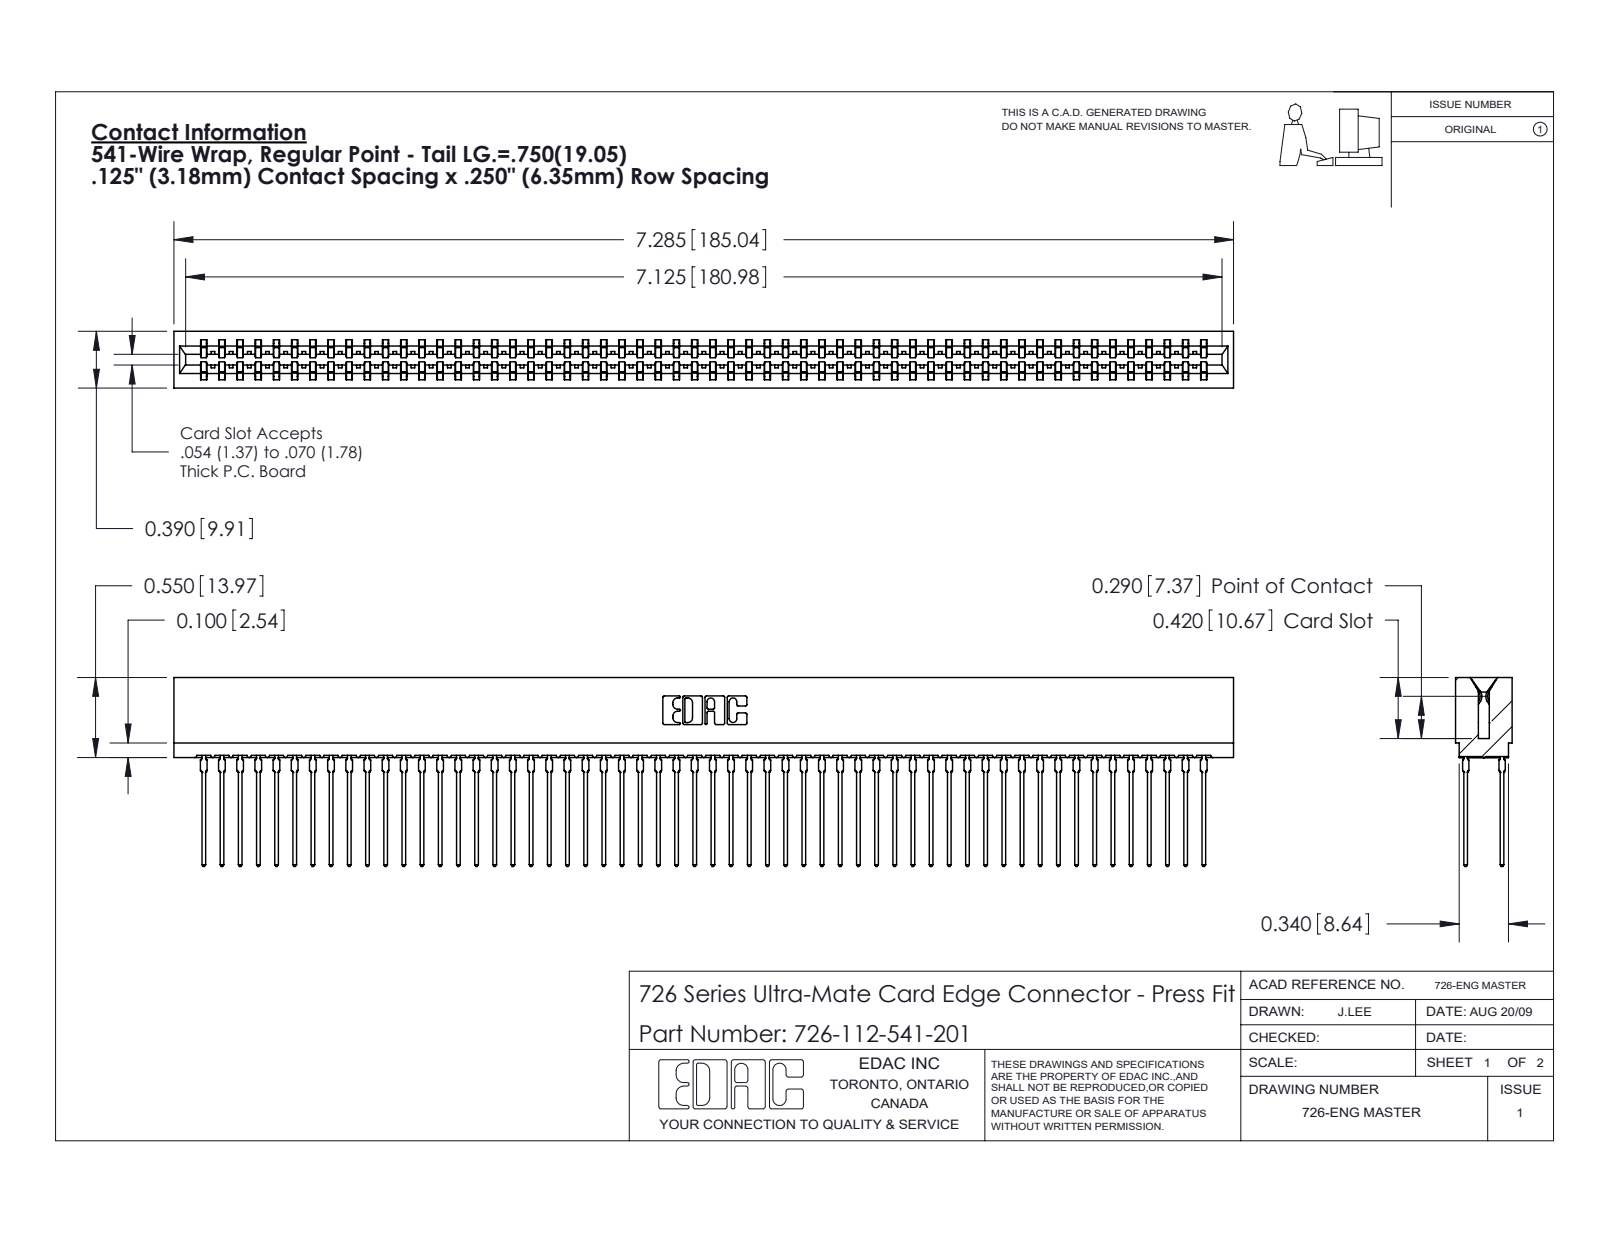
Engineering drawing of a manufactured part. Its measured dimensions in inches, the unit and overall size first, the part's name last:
Units: inches
Overall size (bounding box): 7.285 × 1.299 × 0.39
Partial cylindrical surfaces — rounded edges, fillets, slot ends (radius × count): R0.021 ×224, R0.015 ×57, R0.01 ×22, R0.005 ×8, R0.011 ×8, R0.007 ×6, R0.031 ×6, R0.026 ×3
Main face-to-face distances: 0.057, 0.333, 0.025, 0.307, 0.25, 0.39, 0.083, 0.275, 0.225, 0.365
Volume: 1.072 in³ · Surface area: 50.2 in²
Bodies: 113 solids, 10121 faces (5207 planar, 2002 cylindrical, 2912 other)
Part name (STEP PRODUCT): 746-292-001_541; 726 Part_.515 Slot Depth - 01; 726-112-541-201
STEP written by: SolidWorks 2020 (CONFIG_CONTROL_DESIGN)
